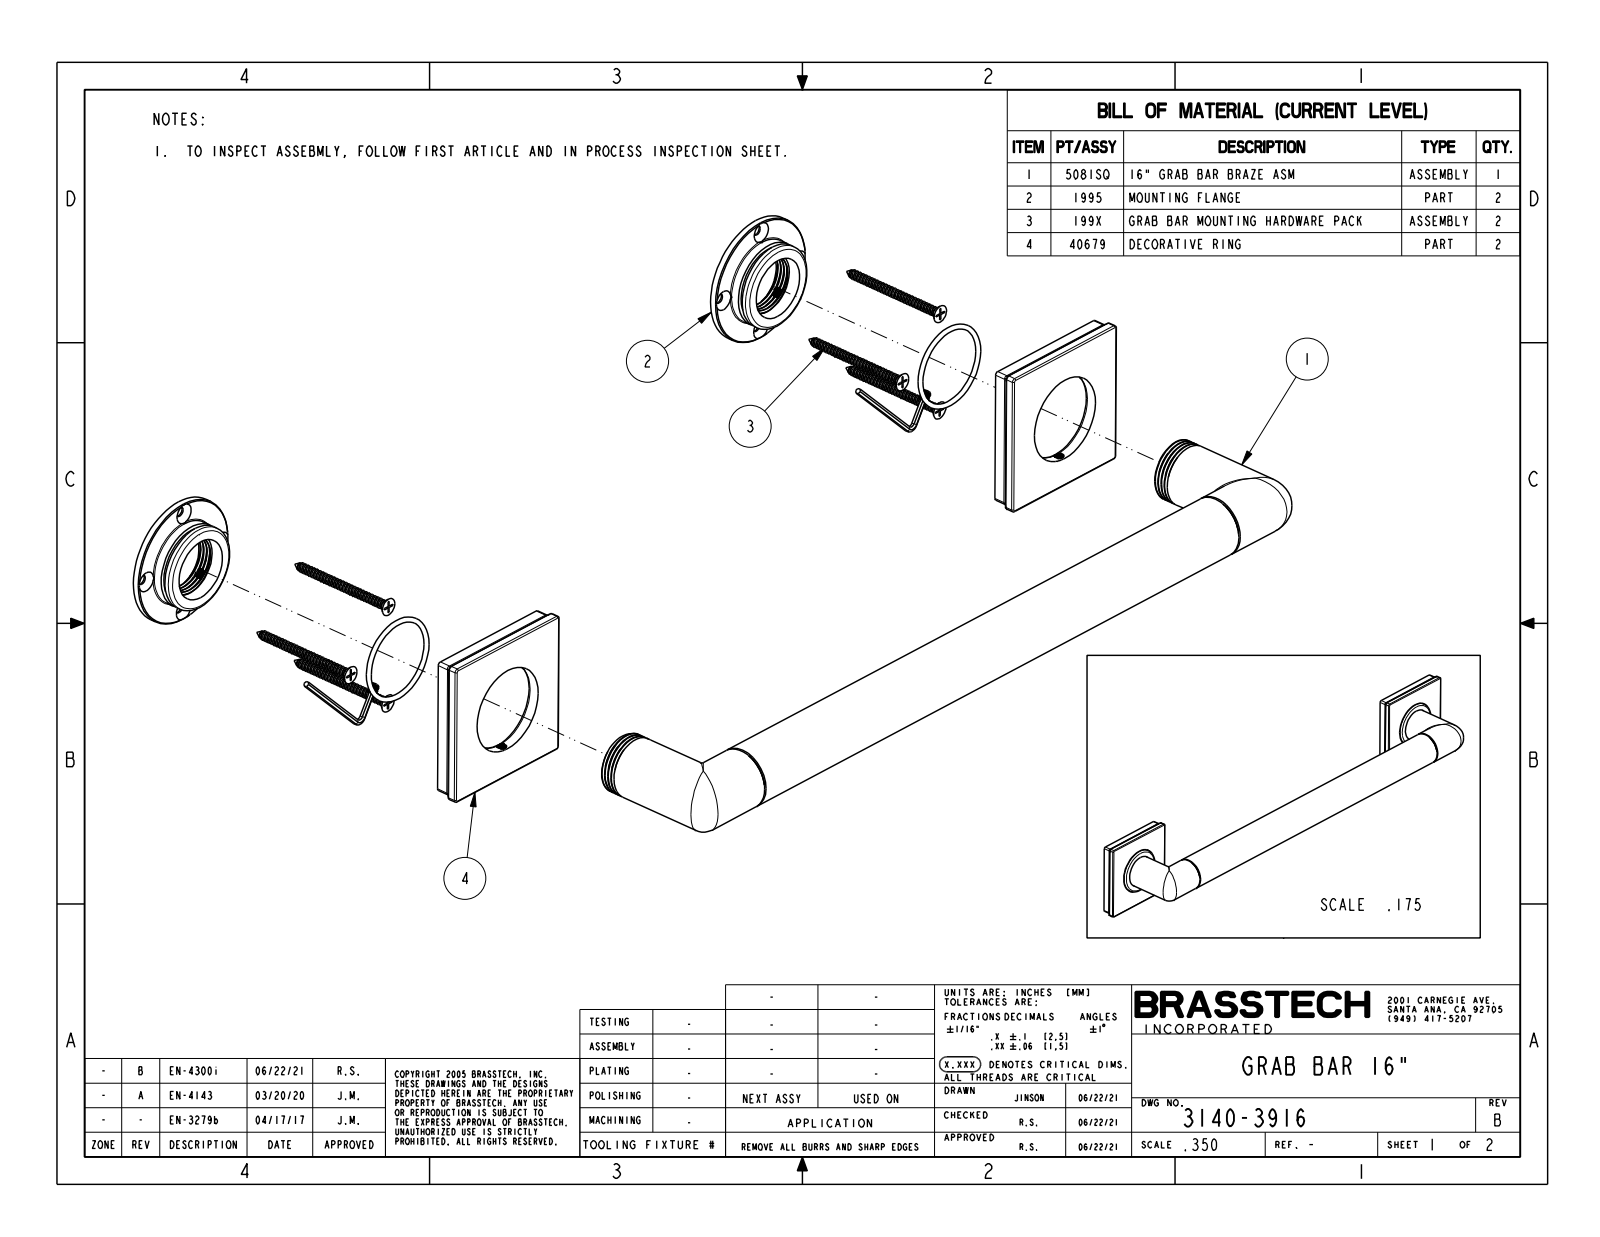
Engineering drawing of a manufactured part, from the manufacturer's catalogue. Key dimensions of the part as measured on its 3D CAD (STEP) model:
Part name (STEP PRODUCT): 3140-3916
STEP written by: CREO PARAMETRIC BY PTC INC, 2018400 (CONFIG_CONTROL_DESIGN)
Units: inches
Bodies: 1 solid, 168 faces (22 planar, 54 cylindrical, 92 other)
Overall size (bounding box): 19 × 3 × 2.755
Volume: 32.78 in³ · Surface area: 119.8 in²
Round bosses / shafts (diameter × count): ⌀1.25 ×3, ⌀1.75 ×2
Partial cylindrical surfaces — rounded edges, fillets, slot ends (radius × count): R0.06 ×16, R0.03 ×12, R0.09 ×6
Main face-to-face distances: 0.525, 0.05, 2.95, 2.9, 16, 3, 0.6, 0.075, 16.05, 18.95
